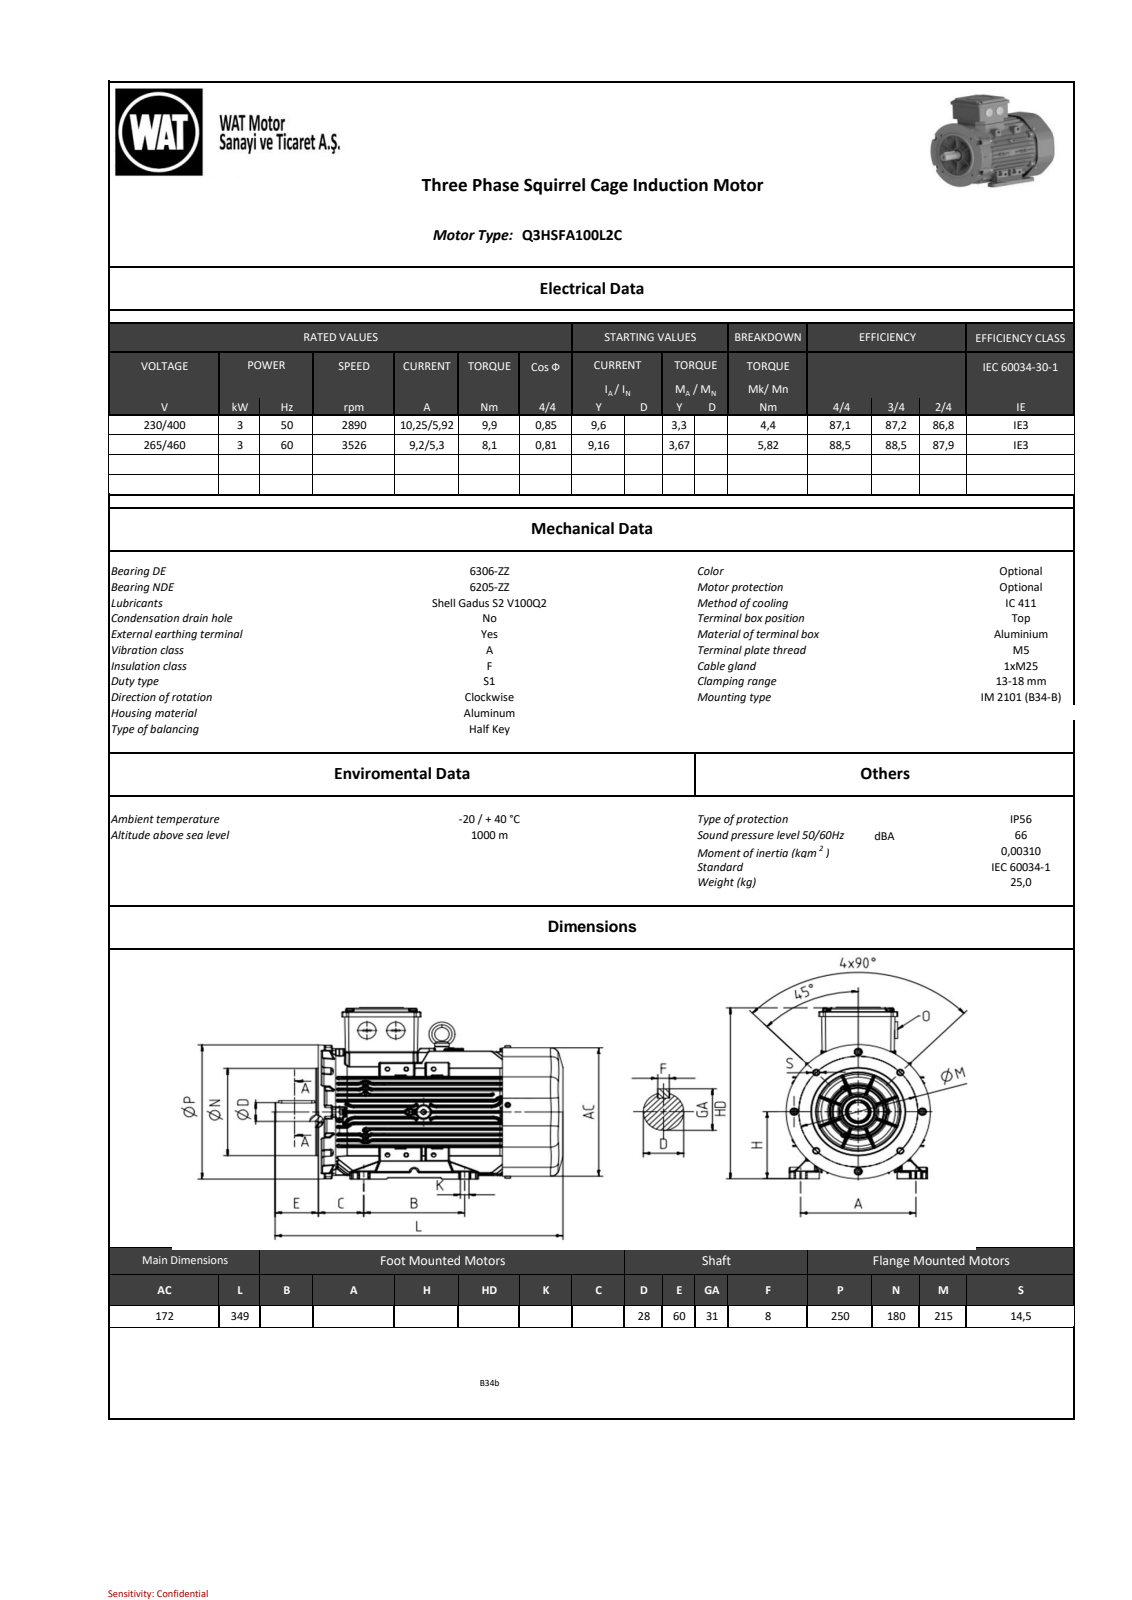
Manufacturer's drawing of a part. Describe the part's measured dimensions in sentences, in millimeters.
The part is named "QHS Series_ 100_B5_stp_objects". Its 3-D file was written by "SIEMENS PLM Software NX2206.8101 (AUTOMOTIVE_DESIGN)". It is 0 solids with 5838 faces: 1366 planar, 2450 cylindrical and 2022 other. Overall it measures 349.04 by 258.21 by 250.32 millimeters. Round holes: 4 of diameter 11, 1 of diameter 9.87, 1 of diameter 79.79, 1 of diameter 97.79, 1 of diameter 115.78. Round bosses or shafts: 7 of diameter 8, 7 of diameter 5, 2 of diameter 25, 1 of diameter 180, 1 of diameter 102.19, 1 of diameter 84.19, 1 of diameter 30, 1 of diameter 28. Partial cylindrical surfaces (rounded edges, fillets, slot ends): 837 of radius 1, 612 of radius 0.8, 65 of radius 2, 43 of radius 0.5, 28 of radius 8, 11 of radius 1.5, 10 of radius 4, 8 of radius 1.6. The main face-to-face distances are 7.5, 16, 91.91, 8.93, 82.98, 23.57, 4, 50.35, 222, 206. The hole center spacings are 112.29, 79.4, 158.8, 79.35, 79.45.
